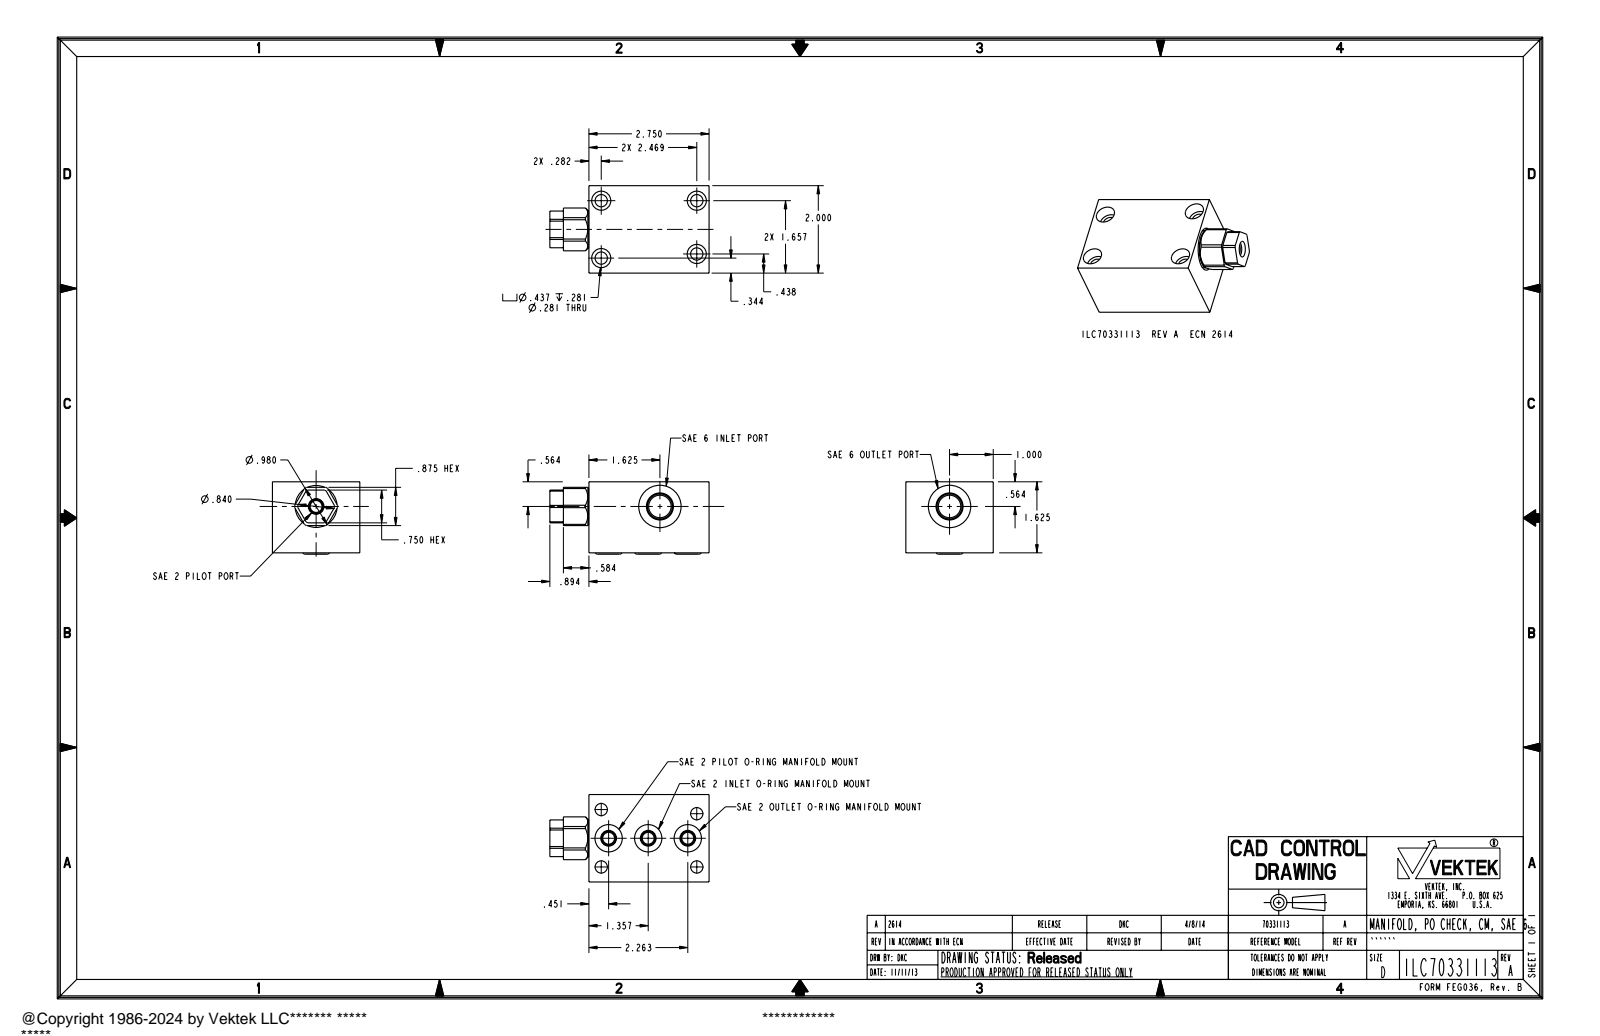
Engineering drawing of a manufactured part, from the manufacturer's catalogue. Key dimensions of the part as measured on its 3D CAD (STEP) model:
Part name (STEP PRODUCT): ILC70331113
STEP written by: PRO/ENGINEER BY PARAMETRIC TECHNOLOGY CORPORATION, 2013320 (AUTOMOTIVE_DESIGN)
Units: inches
Bodies: 1 solid, 141 faces (35 planar, 58 cylindrical, 48 other)
Overall size (bounding box): 3.644 × 2 × 1.656
Volume: 8.411 in³ · Surface area: 41.04 in²
Round holes (diameter × count): ⌀0.272 ×4, ⌀0.281 ×4, ⌀0.437 ×4, ⌀0.625 ×3, ⌀0.515 ×2, ⌀0.97 ×2
Round bosses / shafts (diameter × count): ⌀0.856 ×1
Partial cylindrical surfaces — rounded edges, fillets, slot ends (radius × count): R0.42 ×1, R0.49 ×1
Main face-to-face distances: 1.625, 2, 2.75, 0.875, 0.063, 0.812, 0.105, 1.52, 2.74, 1.99
Hole centre spacings: 0.678, 1.259, 2.087, 0.598, 0.688, 0.906, 0.906, 1.219
